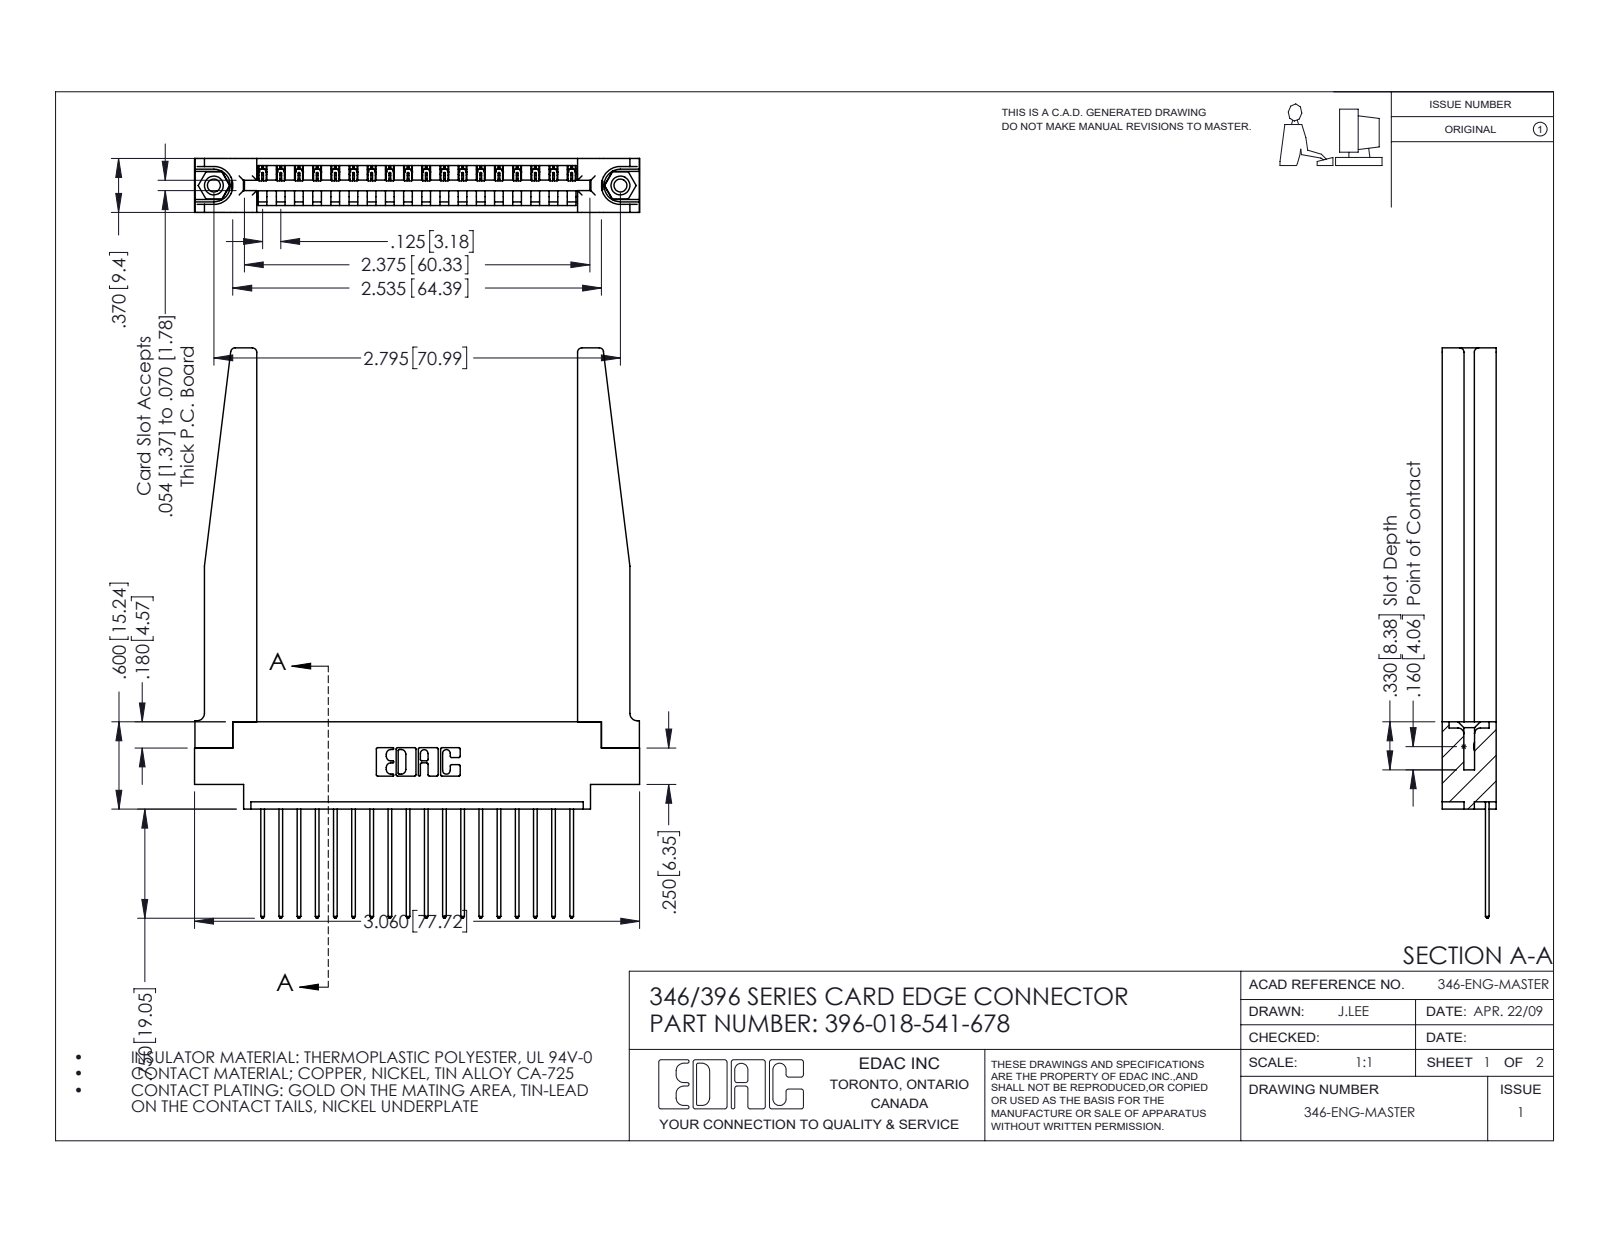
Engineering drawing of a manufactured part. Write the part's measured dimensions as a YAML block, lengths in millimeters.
part_name: "345-292-001_345-293-141; 346 Part_0.170 Offset - 0.156 Dia-TH; 345-250-001_345-250-001-102; 346-220-078_345-220-078 (+1 more)"
step_written_by: "SolidWorks 2016 (CONFIG_CONTROL_DESIGN)"
units: millimeters
bodies: {solids: 23, faces: 1404, planar: 942, cylindrical: 410, other: 52}
overall_size: [99.6, 77.7, 9.4]
volume: 14100
surface_area: 15770
round_holes:
  - {diameter: 2.3, count: 2}
  - {diameter: 3.2, count: 2}
  - {diameter: 4, count: 2}
  - {diameter: 1.6, count: 1}
round_bosses_or_shafts:
  - {diameter: 3.9, count: 2}
partial_cylinders:
  - {radius: 0.2, count: 36}
  - {radius: 0.3, count: 36}
  - {radius: 0.3, count: 22}
  - {radius: 0.8, count: 8}
  - {radius: 0.2, count: 6}
  - {radius: 0.8, count: 6}
  - {radius: 0.7, count: 3}
  - {radius: 0.8, count: 2}
face_to_face_distances: [9.4, 1.8, 1.2, 8.2, 3.8, 3.8, 6.4, 7.6, 0.6, 2.6]
hole_center_spacings: [6.2, 65.7, 71]
